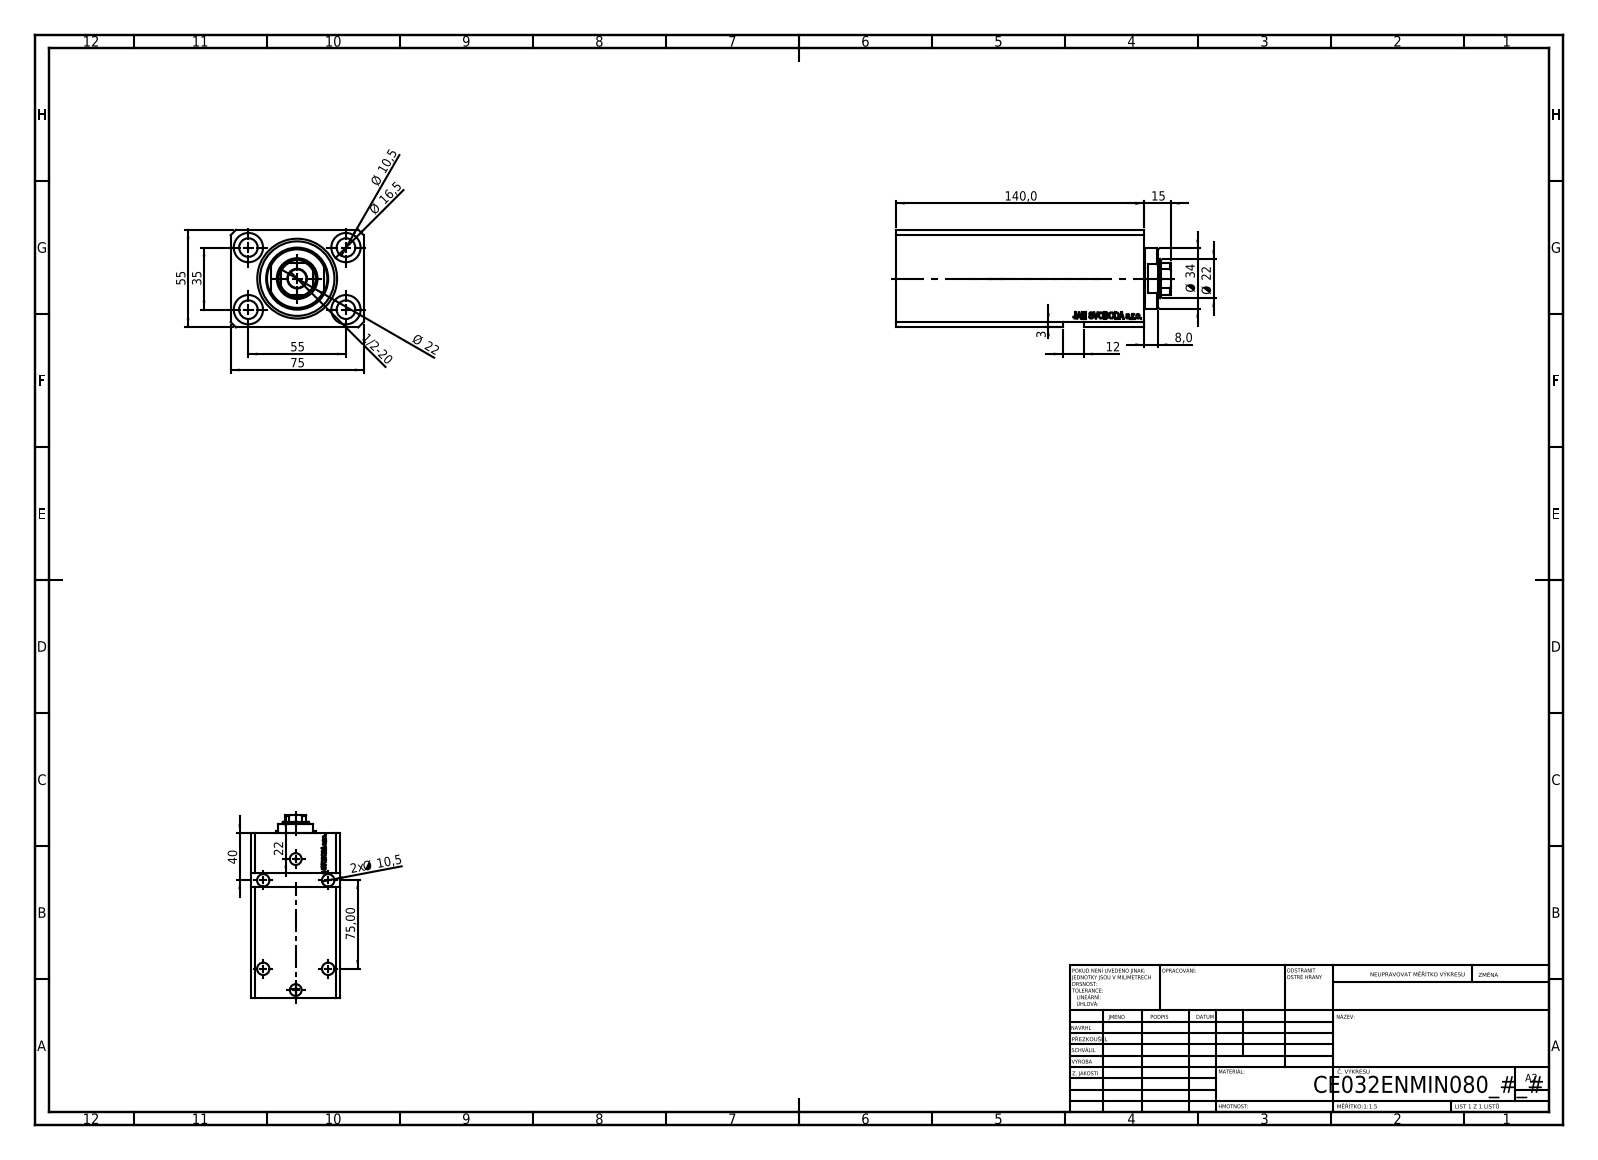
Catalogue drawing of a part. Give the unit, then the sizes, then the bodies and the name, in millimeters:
Units: millimetres
Overall size (bounding box): 155 × 75 × 55
Round holes (diameter × count): ⌀10.5 ×9, ⌀1.25 ×4, ⌀16.5 ×4, ⌀10 ×2, ⌀13.16 ×2, ⌀20 ×2, ⌀22 ×1, ⌀32 ×1, ⌀45 ×1
Round bosses / shafts (diameter × count): ⌀34 ×1
Partial cylindrical surfaces — rounded edges, fillets, slot ends (radius × count): R10.5 ×1
Main face-to-face distances: 55, 75, 15, 140, 125, 9.9, 115.1, 130.1, 11, 129
Hole centre spacings: 32.6, 32.87, 55, 96.98, 32.58, 35, 65.19, 75
Volume: 469 209 mm³ · Surface area: 102 026 mm²
Bodies: 3 solids, 914 faces (438 planar, 104 cylindrical, 372 other)
Part name (STEP PRODUCT): V250CE_VC_E; V250CE_C_VCP; V250CE_E_Body
STEP written by: SolidWorks 2019 (CONFIG_CONTROL_DESIGN)
